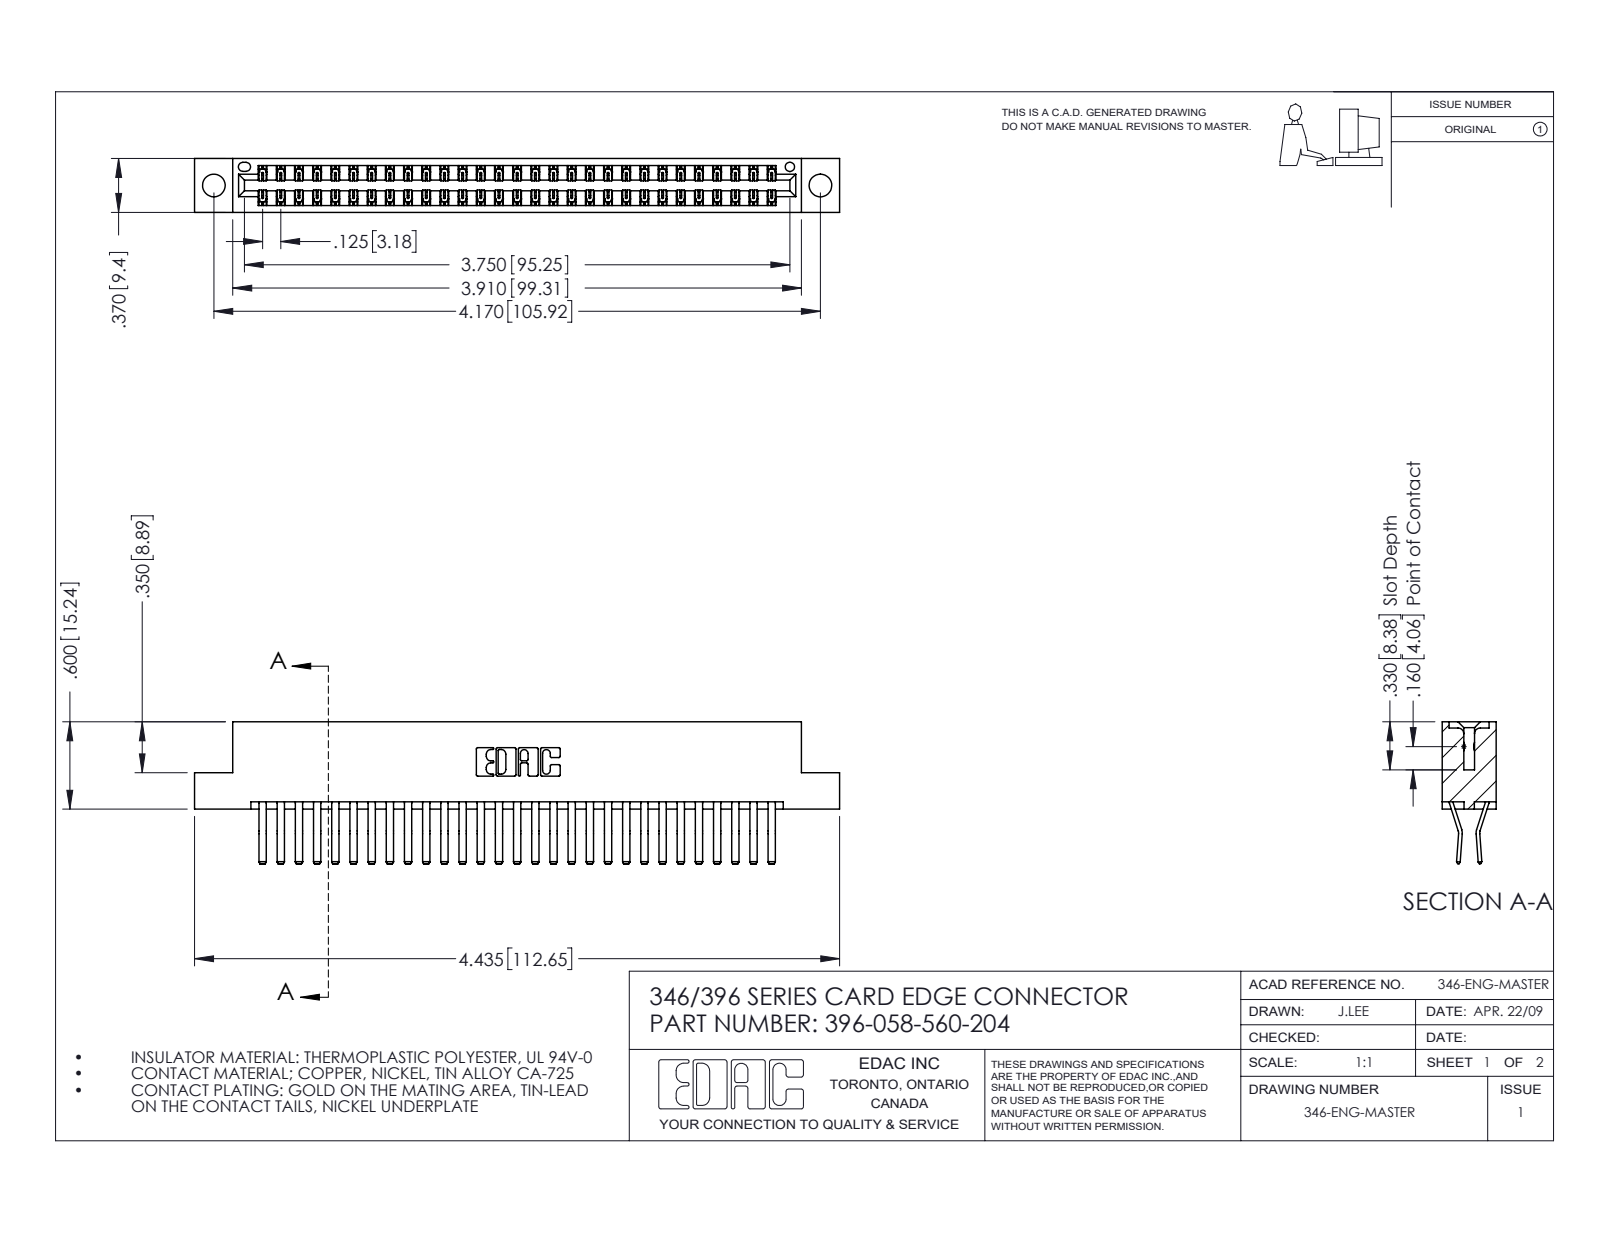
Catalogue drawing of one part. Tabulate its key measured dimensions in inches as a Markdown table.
| quantity | value |
| --- | --- |
| part name | 346 Part_Flush Mounting Lugs - 0.156 Dia-TH; 396-058-560-204; 345-292-001_560 Tail |
| STEP written by | SolidWorks 2016 (CONFIG_CONTROL_DESIGN) |
| units | inches |
| bodies | 59 solids, 3254 faces (2106 planar, 1148 cylindrical, 0 other) |
| overall size | 4.435 × 0.975 × 0.37 |
| volume | 0.682 in³ |
| surface area | 24.78 in² |
| round holes (diameter × count) | 0.156 × 2, 0.064 × 1 |
| partial cylindrical surfaces (radius × count) | 0.006 × 87, 0.01 × 22, 0.007 × 6, 0.031 × 6, 0.026 × 3, 0.01 × 2, 0.014 × 2, 0.022 × 2 |
| main face-to-face distances | 0.048, 0.322, 0.37, 0.25, 0.025, 0.072, 0.298, 0.275, 0.148, 0.222 |
| hole center spacings | 0.246, 3.962, 4.17 |
